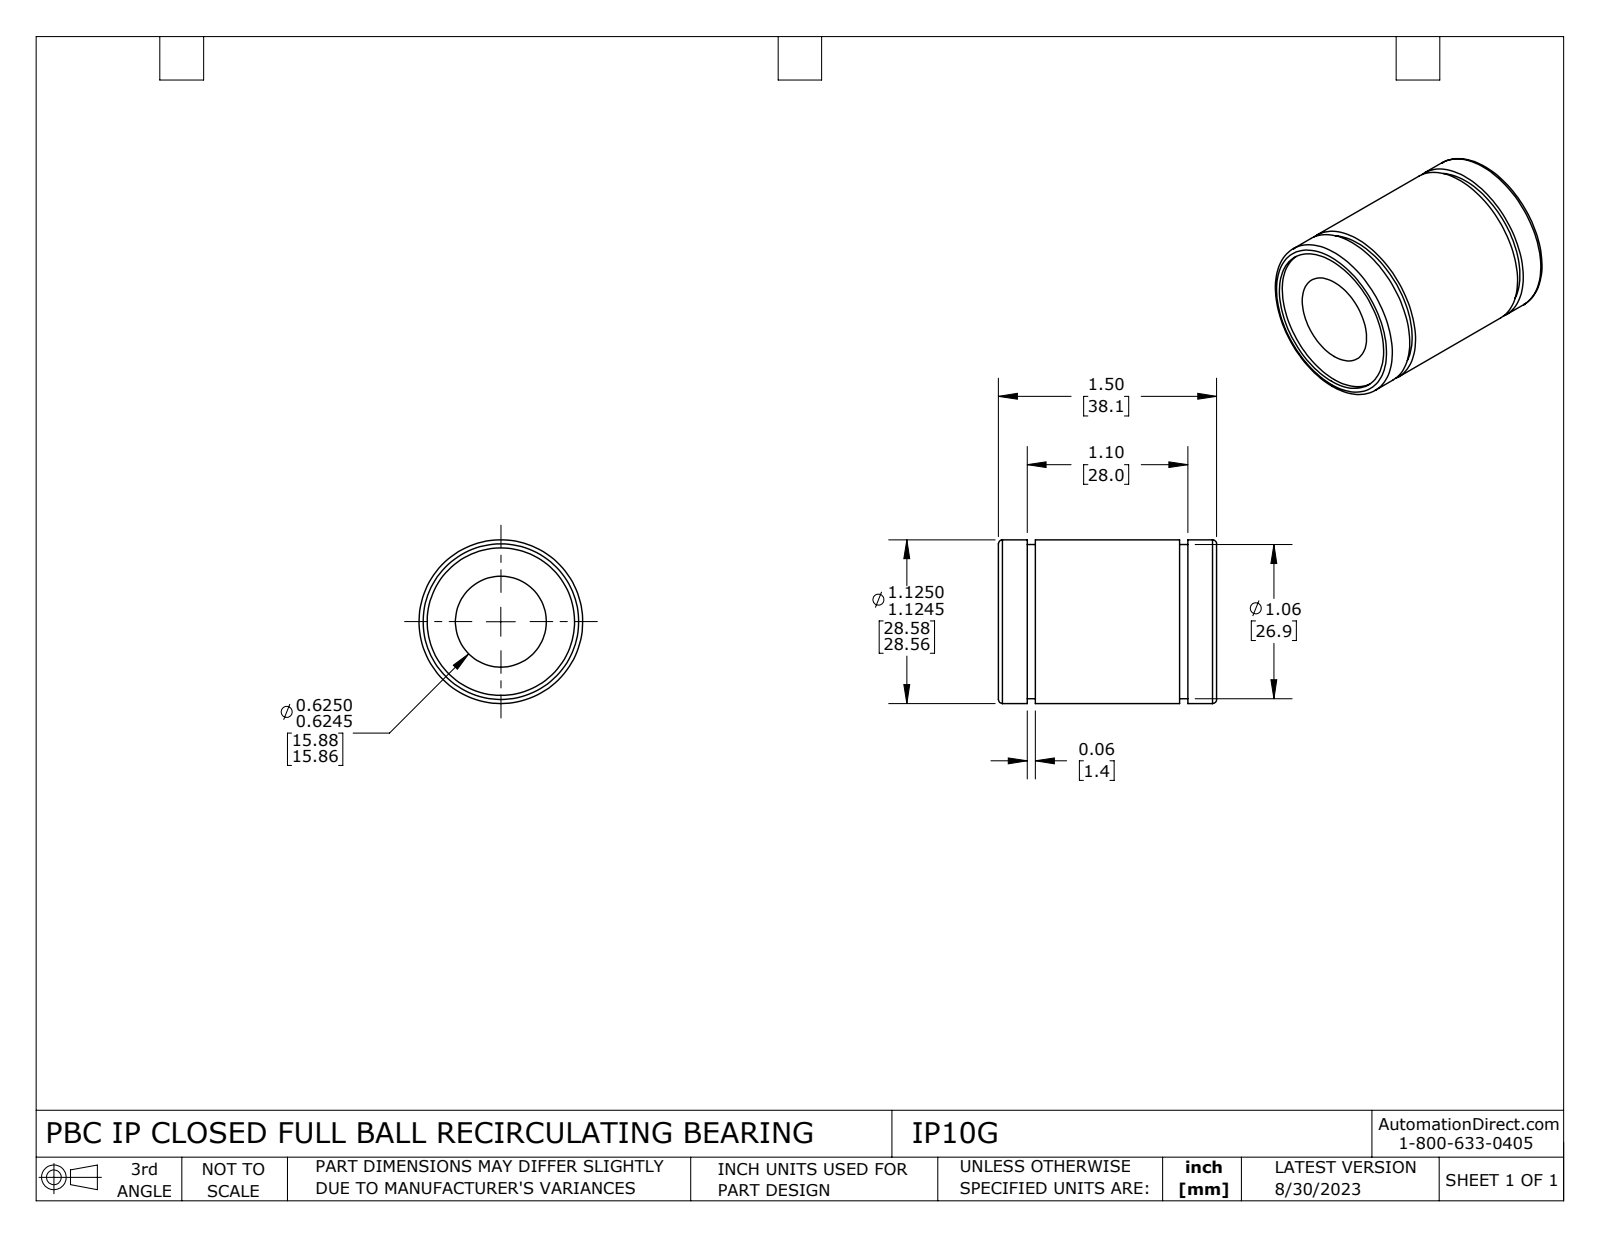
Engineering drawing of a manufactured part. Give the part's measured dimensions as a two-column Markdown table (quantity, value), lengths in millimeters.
| quantity | value |
| --- | --- |
| part name | IP10G |
| STEP written by | SolidWorks 2021 (CONFIG_CONTROL_DESIGN) |
| units | millimeters |
| bodies | 1 solid, 28 faces (8 planar, 16 cylindrical, 4 other) |
| overall size | 38.1 × 28.6 × 28.6 |
| volume | 16 200 mm³ |
| surface area | 6 471 mm² |
| round holes (diameter × count) | 15.9 × 1, 25.7 × 1 |
| round bosses / shafts (diameter × count) | 28.6 × 1, 26.9 × 1 |
| main face-to-face distances | 36.7, 4.3, 5.7, 30.9, 32.4, 26.6, 1.4, 0.7, 5, 6.5 |
